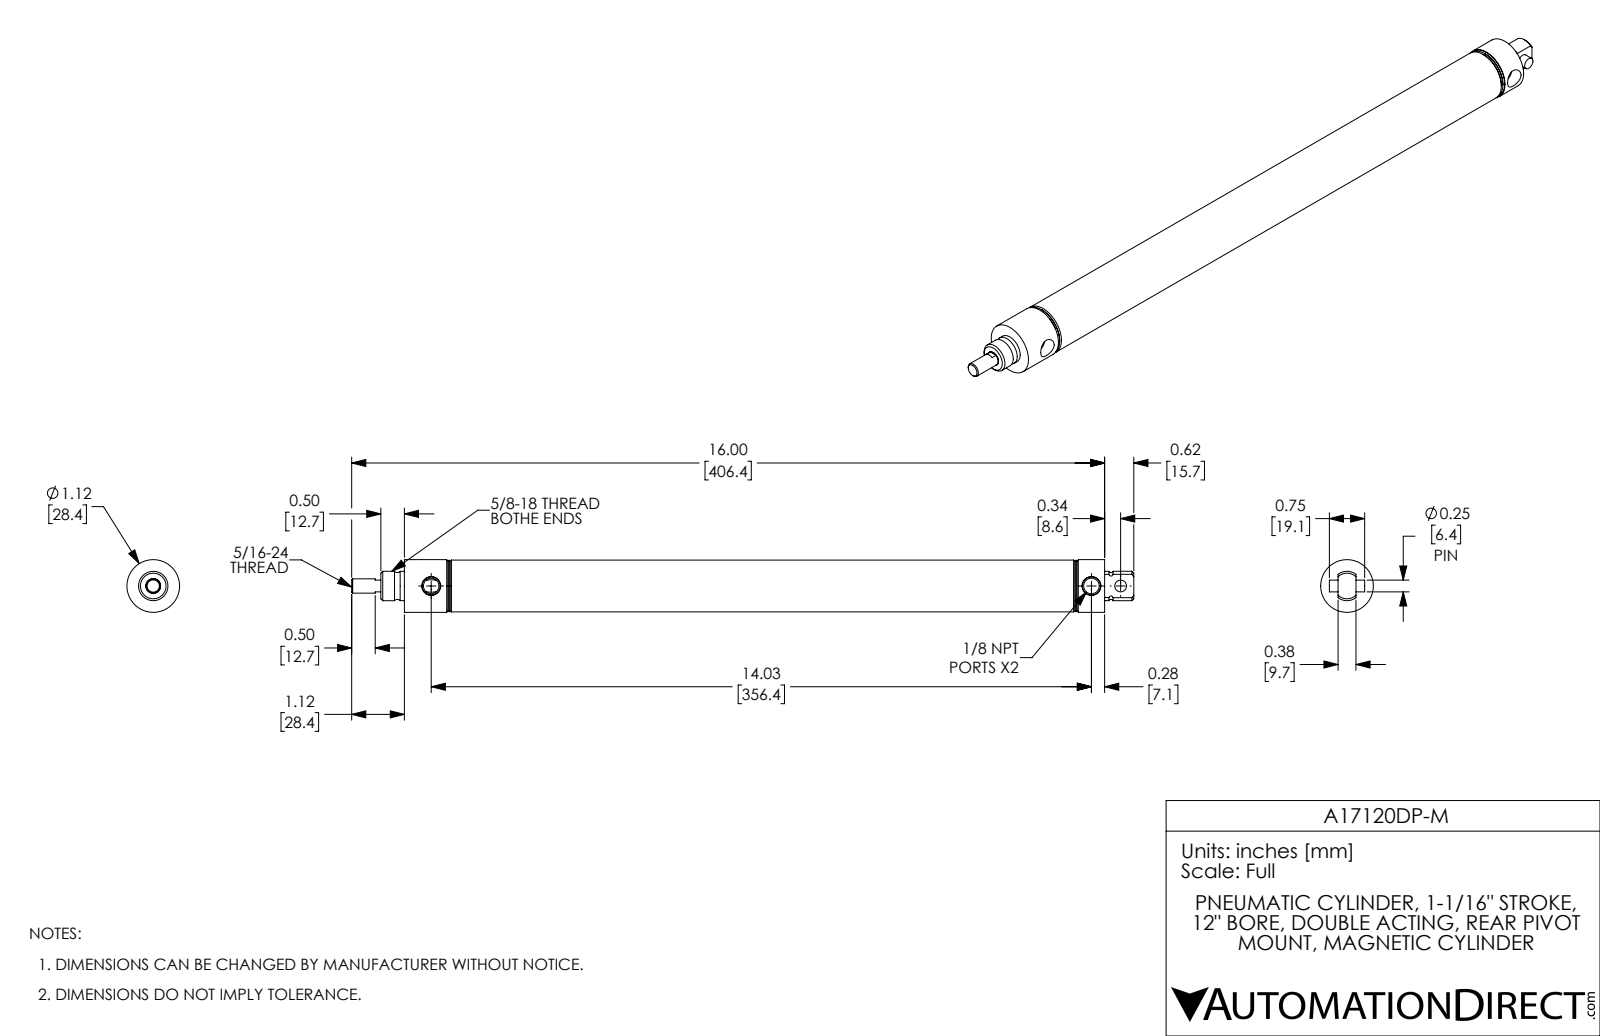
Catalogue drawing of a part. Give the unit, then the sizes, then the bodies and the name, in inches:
Units: inches
Overall size (bounding box): 16.62 × 1.12 × 1.12
Round holes (diameter × count): ⌀0.332 ×2, ⌀0.25 ×1, ⌀0.312 ×1, ⌀1.063 ×1
Round bosses / shafts (diameter × count): ⌀1.12 ×1, ⌀1.1 ×1, ⌀0.625 ×1, ⌀0.623 ×1, ⌀0.304 ×1
Partial cylindrical surfaces — rounded edges, fillets, slot ends (radius × count): R0.313 ×1
Main face-to-face distances: 0.5, 13.69, 12.5, 12, 1.19, 1.69, 13.69, 14.88, 13.19, 1.19
Hole centre spacings: 0.62, 14.03, 14.65
Volume: 4.708 in³ · Surface area: 120 in²
Bodies: 3 solids, 92 faces (22 planar, 32 cylindrical, 38 other)
Part name (STEP PRODUCT): A17120DP-M-PIN; A17120DP-M-Rod; A17120DP-M-MainBody; A17120DP-M
STEP written by: SolidWorks 2017 (AUTOMOTIVE_DESIGN)
